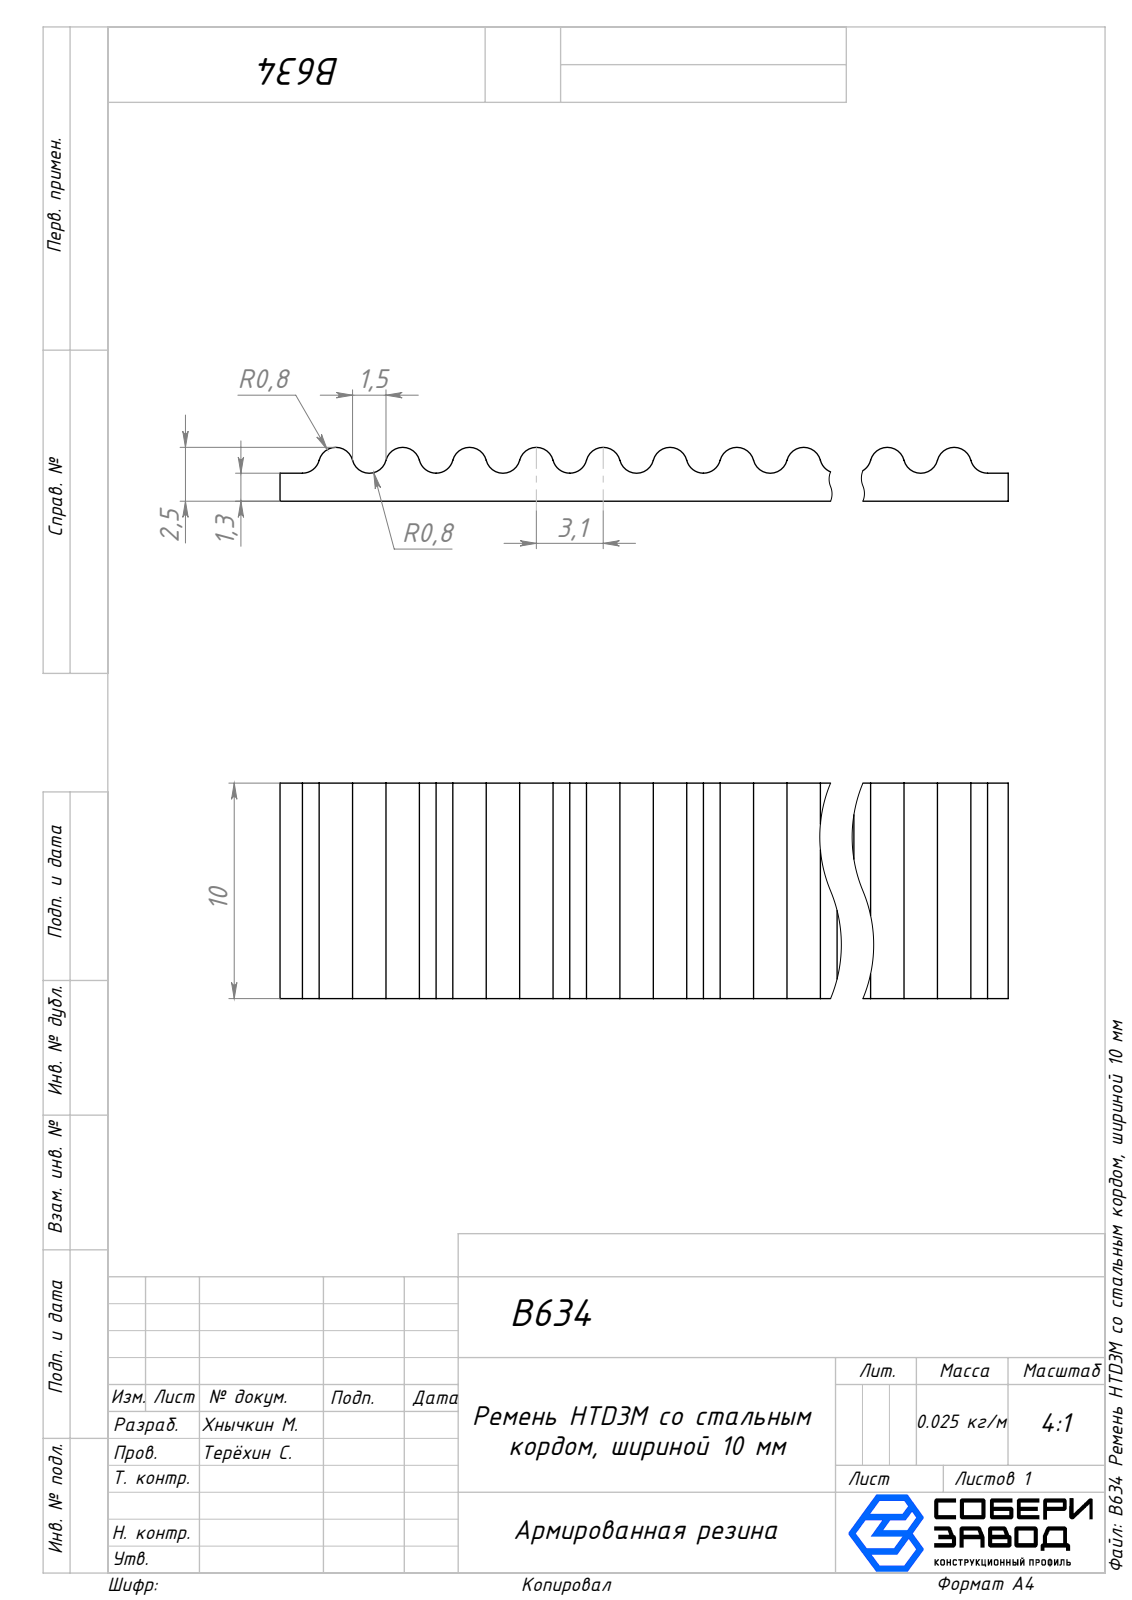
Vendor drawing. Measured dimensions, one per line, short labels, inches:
name: B634 Ремень HTD3M со стальным кордом, шириной 10 мм
written by: SolidWorks 2025 (AUTOMOTIVE_DESIGN)
unit: in
bodies: 1 solid, 32 faces (7 planar, 25 cylindrical, 0 other)
size: 1.299 × 0.394 × 0.098
volume: 0.038 in³; area: 1.43 in²
rounds: 22× R0.031
face distances: 0.394, 0.051, 1.299
